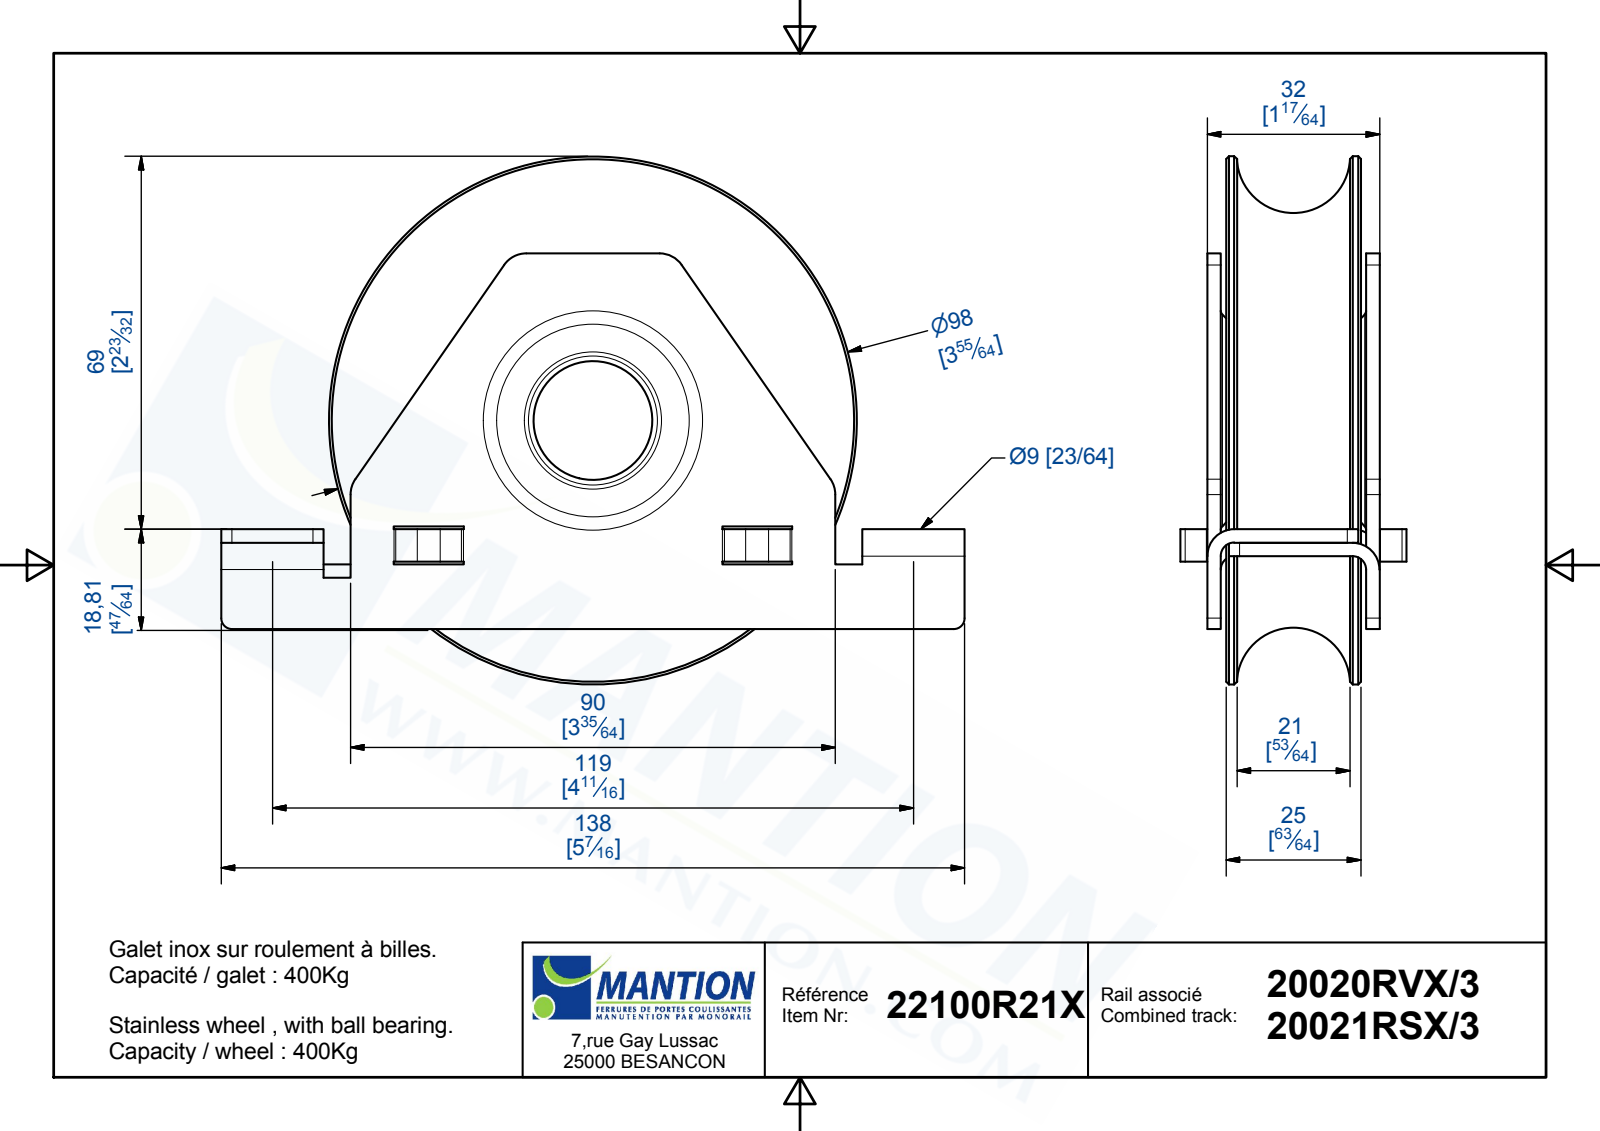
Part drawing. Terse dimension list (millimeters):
name: 22100R21X; 22686; 20219; 20221 monte (+1 more)
written by: Autodesk Inventor 2019 (AUTOMOTIVE_DESIGN)
unit: mm
bodies: 11 solids, 212 faces (107 planar, 61 cylindrical, 44 other)
size: 138 × 98 × 36.02
volume: 148 228 mm³; area: 67 402 mm²
holes: 2× ⌀9, 1× ⌀13.9, 1× ⌀17, 1× ⌀17.2, 1× ⌀37.22, 1× ⌀41, 1× ⌀47, 1× ⌀47.4, 1× ⌀52
bosses: 1× ⌀98, 1× ⌀26.78, 1× ⌀22, 1× ⌀16.9
rounds: 8× R5, 4× R1, 4× R2.5, 2× R2
face distances: 2.5, 3.5, 26, 1, 28.5, 29.5, 25, 27, 32, 6.5
hole spacings: 119
